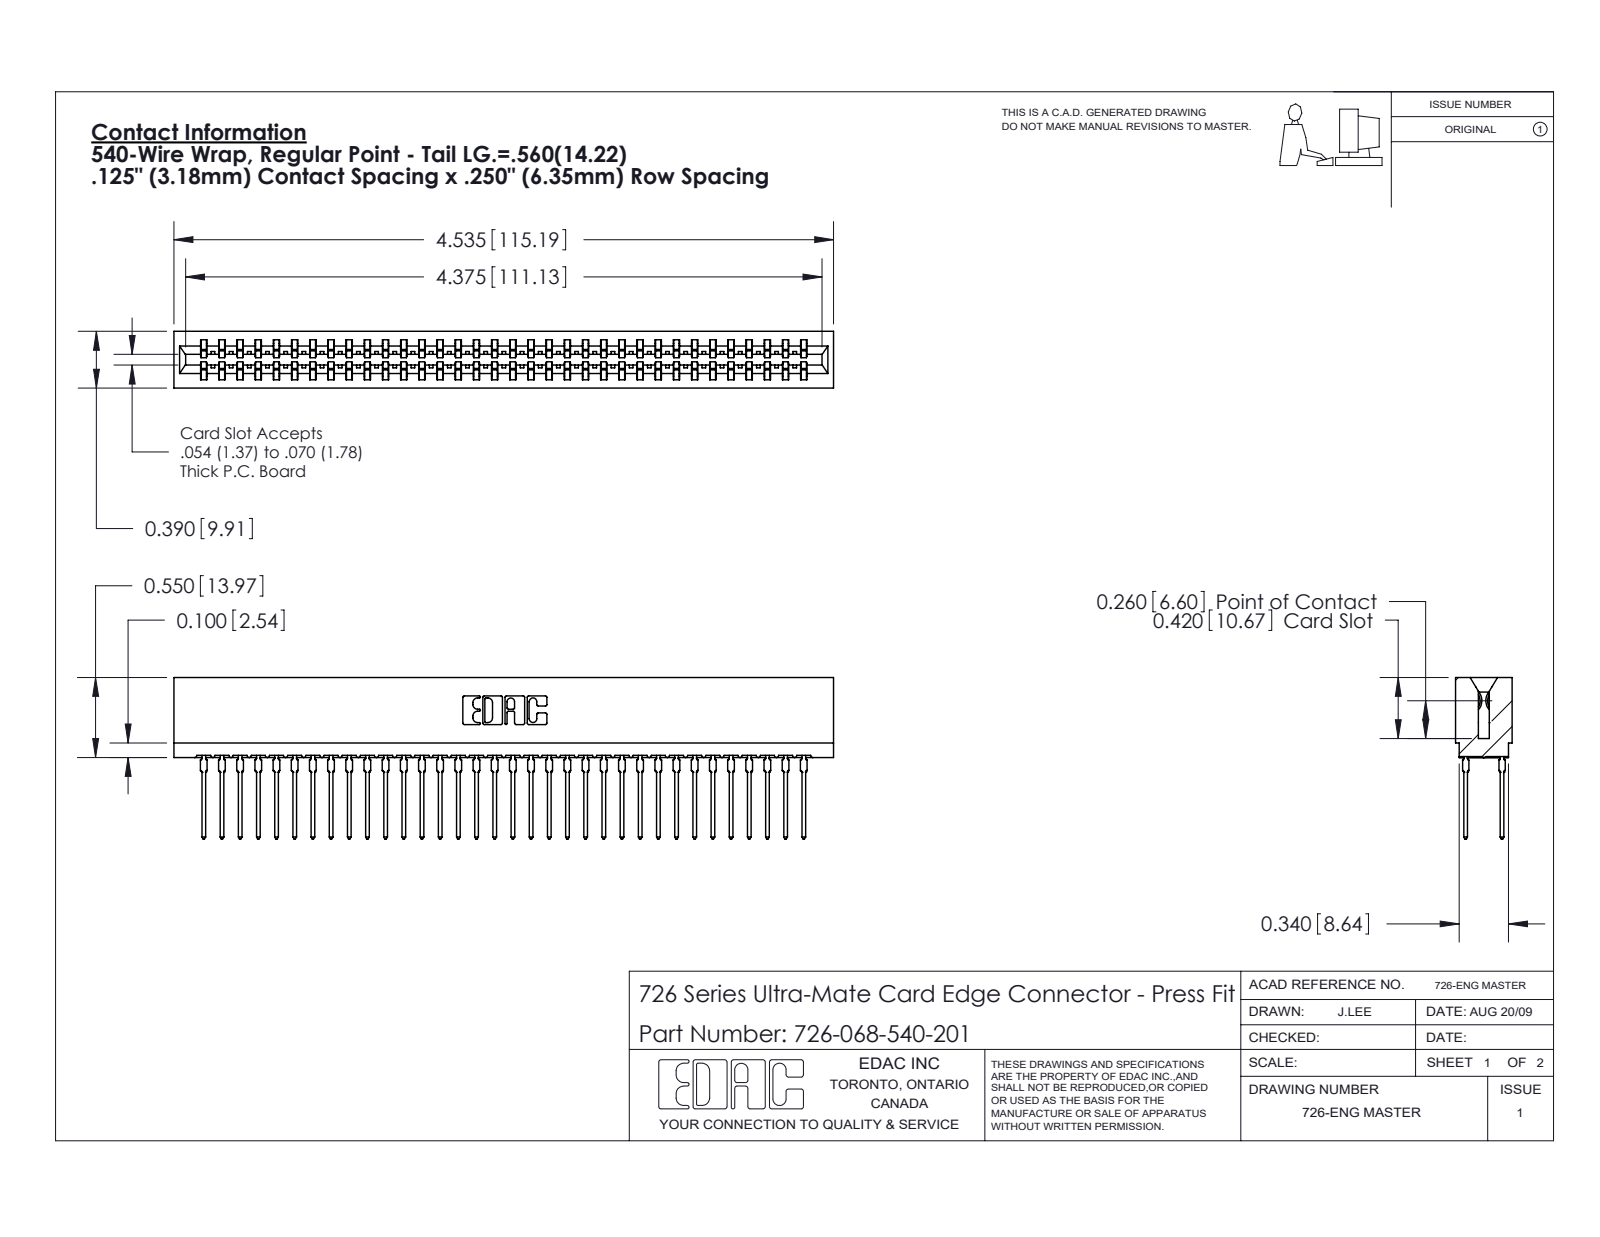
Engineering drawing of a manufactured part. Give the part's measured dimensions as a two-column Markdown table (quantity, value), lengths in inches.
| quantity | value |
| --- | --- |
| part name | 726 Part_.515 Slot Depth - 01; 726-068-540-201; 746-292-001_540 |
| STEP written by | SolidWorks 2020 (CONFIG_CONTROL_DESIGN) |
| units | inches |
| bodies | 69 solids, 6183 faces (3183 planar, 1232 cylindrical, 1768 other) |
| overall size | 4.535 × 1.109 × 0.39 |
| volume | 0.662 in³ |
| surface area | 29.28 in² |
| partial cylindrical surfaces (radius × count) | 0.021 × 136, 0.015 × 35, 0.01 × 22, 0.005 × 8, 0.011 × 8, 0.007 × 6, 0.031 × 6, 0.026 × 3 |
| main face-to-face distances | 0.057, 0.333, 0.025, 0.307, 0.25, 0.39, 0.083, 0.275, 0.365, 0.032 |
